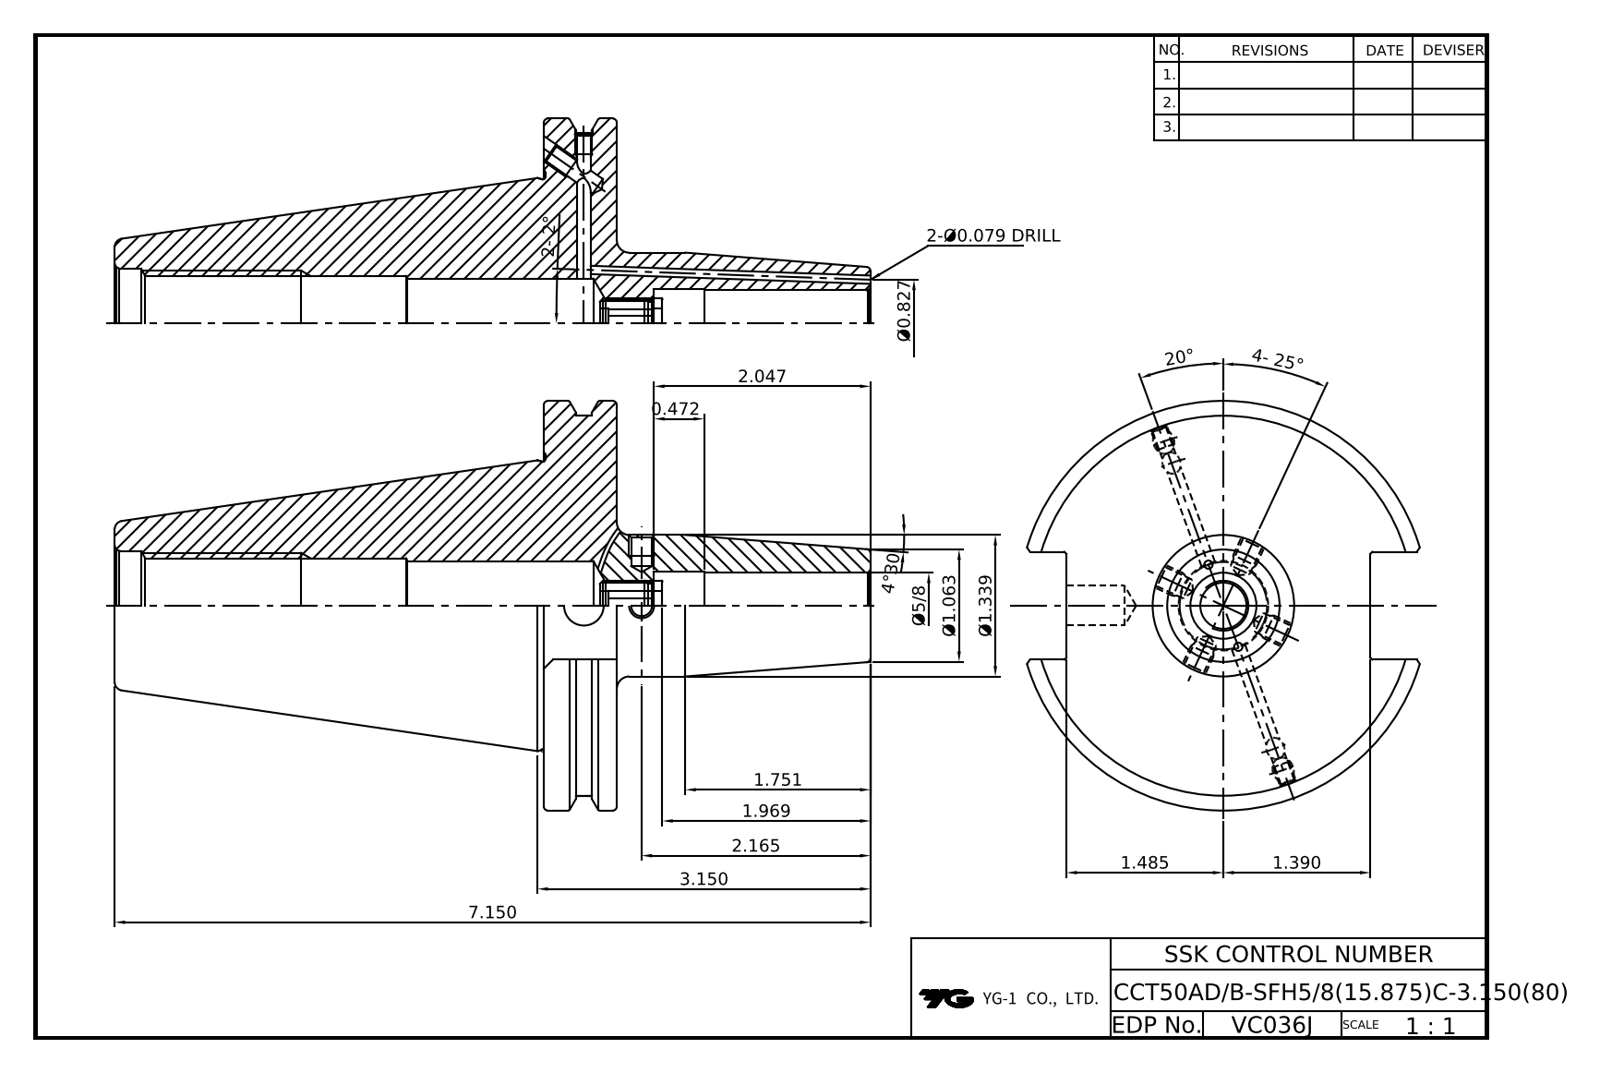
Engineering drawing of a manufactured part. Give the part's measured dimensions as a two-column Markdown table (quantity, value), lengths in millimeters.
| quantity | value |
| --- | --- |
| part name | LO-CCT50ADB-SFH15.875C-3.15(20240115) |
| STEP written by | Autodesk Inventor 2024 (AUTOMOTIVE_DESIGN) |
| units | millimeters |
| bodies | 1 solid, 92 faces (38 planar, 29 cylindrical, 25 other) |
| overall size | 181.6 × 98.42 × 94.69 |
| volume | 360 851 mm³ |
| surface area | 54 460 mm² |
| round holes (diameter × count) | 2.5 × 2, 3.24 × 2, 4.13 × 2, 4.2 × 2, 5 × 2, 9.53 × 1, 10.92 × 1, 15.88 × 1, 17.07 × 1, 21.5 × 1, 21.97 × 1, 26.2 × 1 |
| round bosses / shafts (diameter × count) | 98.42 × 1, 91.29 × 1, 69.25 × 1, 34 × 1 |
| main face-to-face distances | 17.55, 103.1, 120.65, 73.03, 25.9, 181.6, 78.5, 60.95, 103.5, 0.4 |
